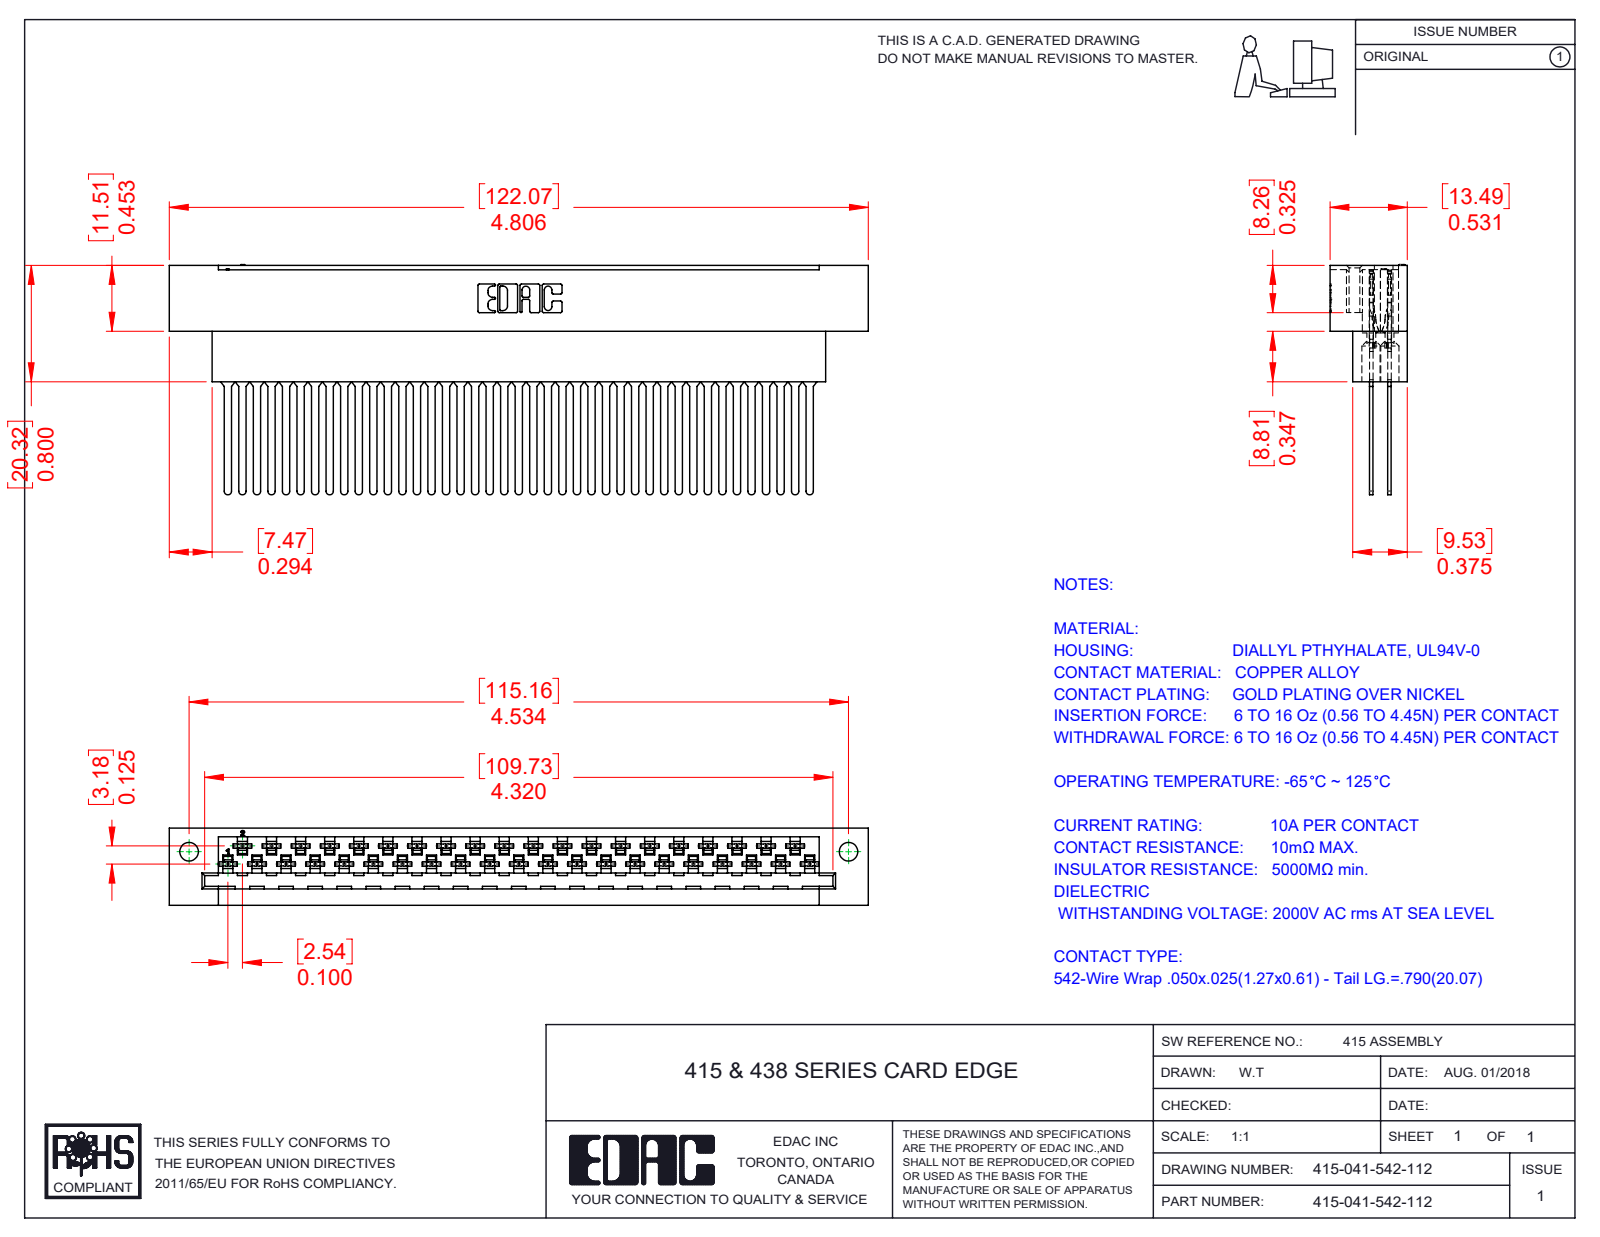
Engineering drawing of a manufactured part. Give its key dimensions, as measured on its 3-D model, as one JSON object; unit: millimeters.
{"part_name": "415-210-001_415-210-041-112; 516-290-001_542; 415-041-542-112", "step_written_by": "SolidWorks 2016 (CONFIG_CONTROL_DESIGN)", "units": "millimeters", "bodies": {"solids": 42, "faces": 4162, "planar": 2661, "cylindrical": 1110, "other": 391}, "overall_size": [122.07, 40.17, 13.49], "volume_mm3": 21139, "surface_area_mm2": 28153, "round_holes": [[1.27, 41], [3.3, 41], [3.25, 2]], "partial_cylinders_radius": [[0.3, 164], [0.56, 164], [0.18, 82], [0.2, 82], [0.41, 82], [2.03, 82], [0.64, 41], [0.25, 22]], "face_to_face_distances": [3.18, 0.61, 1.88, 7.49, 6.61, 6, 1.27, 2.82, 3.79, 3.43], "hole_center_spacings": [5.08, 10.16, 15.24, 20.32, 25.4, 30.48, 35.56, 2.54]}
